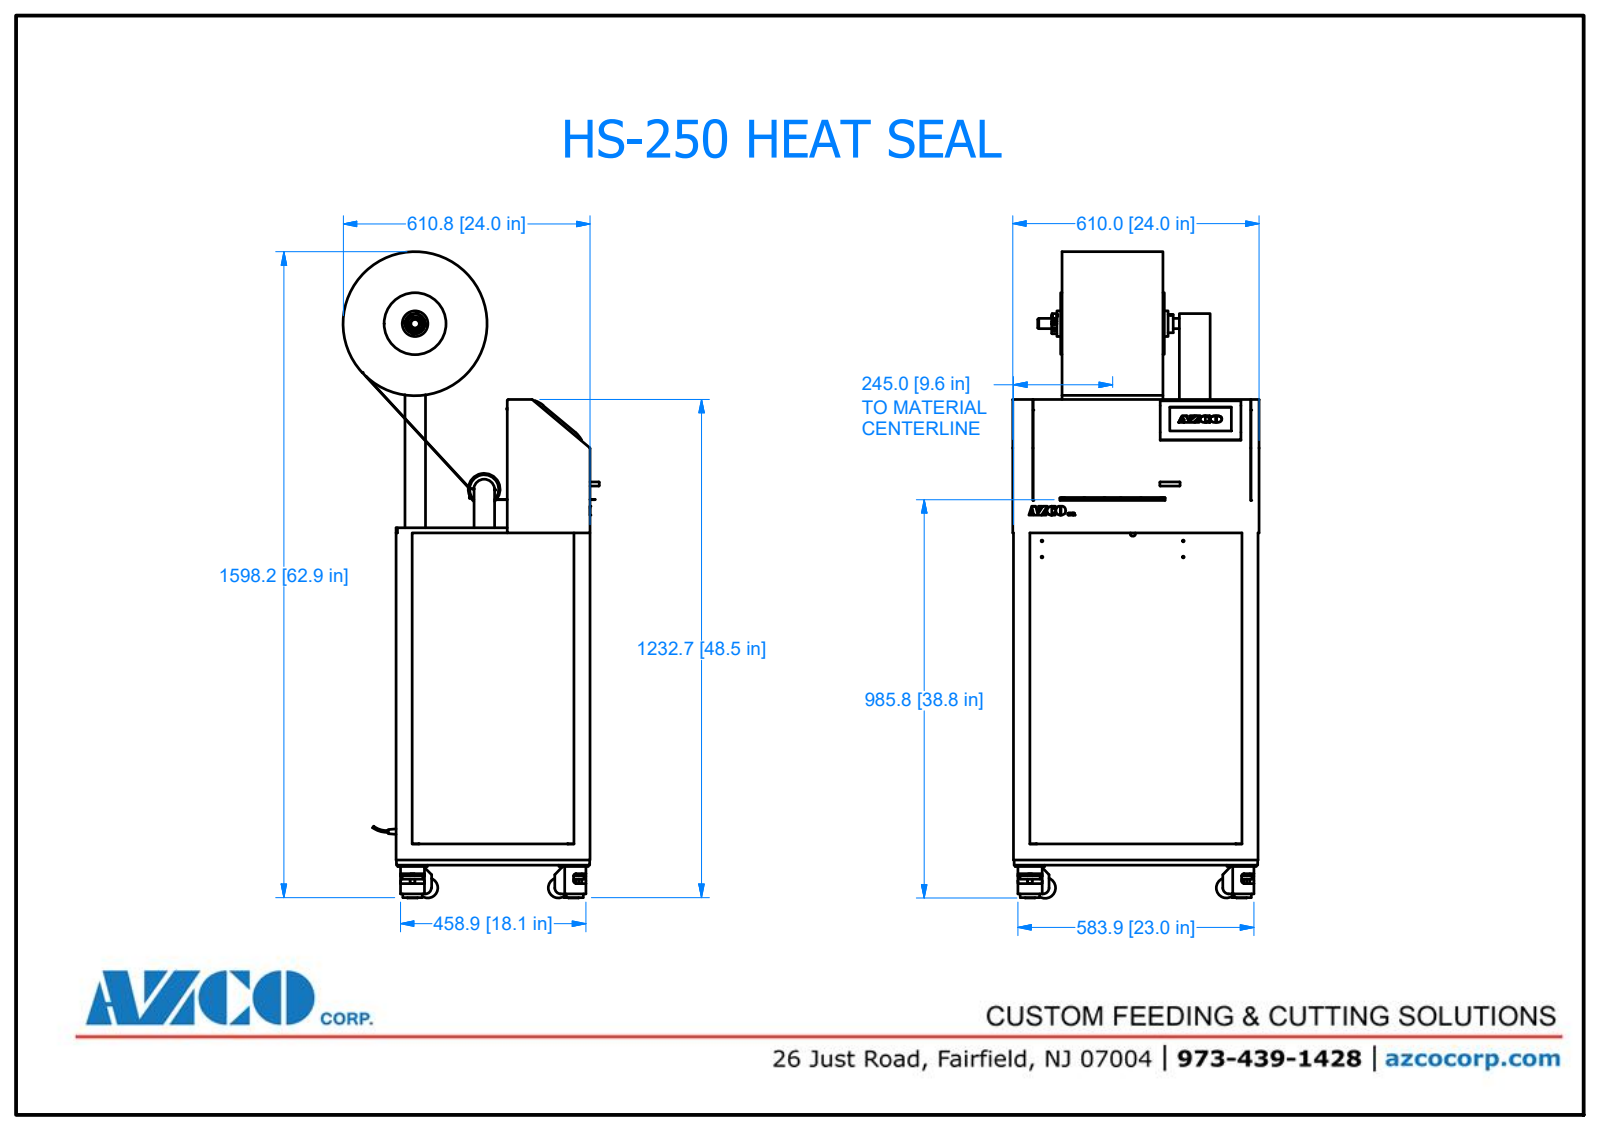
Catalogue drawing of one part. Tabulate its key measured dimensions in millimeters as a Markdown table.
| quantity | value |
| --- | --- |
| part name | HS250-02 SOLID MODEL |
| STEP written by | Autodesk Inventor 2016 (AUTOMOTIVE_DESIGN) |
| units | millimeters |
| bodies | 9 solids, 2685 faces (1515 planar, 582 cylindrical, 588 other) |
| overall size | 1599.48 × 633.66 × 610 |
| volume | 52 530 000 mm³ |
| surface area | 7 719 000 mm² |
| round holes (diameter × count) | 4.92 × 36, 3.24 × 30, 9 × 21, 4.5 × 18, 6.6 × 18, 6.65 × 18, 6.35 × 16, 4.13 × 13, 15 × 10, 6.5 × 8, 5 × 6, 8.25 × 6 |
| round bosses / shafts (diameter × count) | 50.8 × 4, 6 × 4, 11 × 2, 355.6 × 1, 152.4 × 1, 88.9 × 1, 78 × 1, 63.5 × 1 |
| partial cylindrical surfaces (radius × count) | 5 × 18, 6 × 16, 1 × 13, 4 × 12, 2 × 8, 7 × 8, 3 × 7, 25 × 6 |
| main face-to-face distances | 6.35, 440, 12.7, 822.7, 433.65, 446.35, 1.52, 3.17, 23.17, 16.82 |
| hole center spacings | 28, 39.6, 25.08, 58.06, 56, 370, 10, 11.37 |
